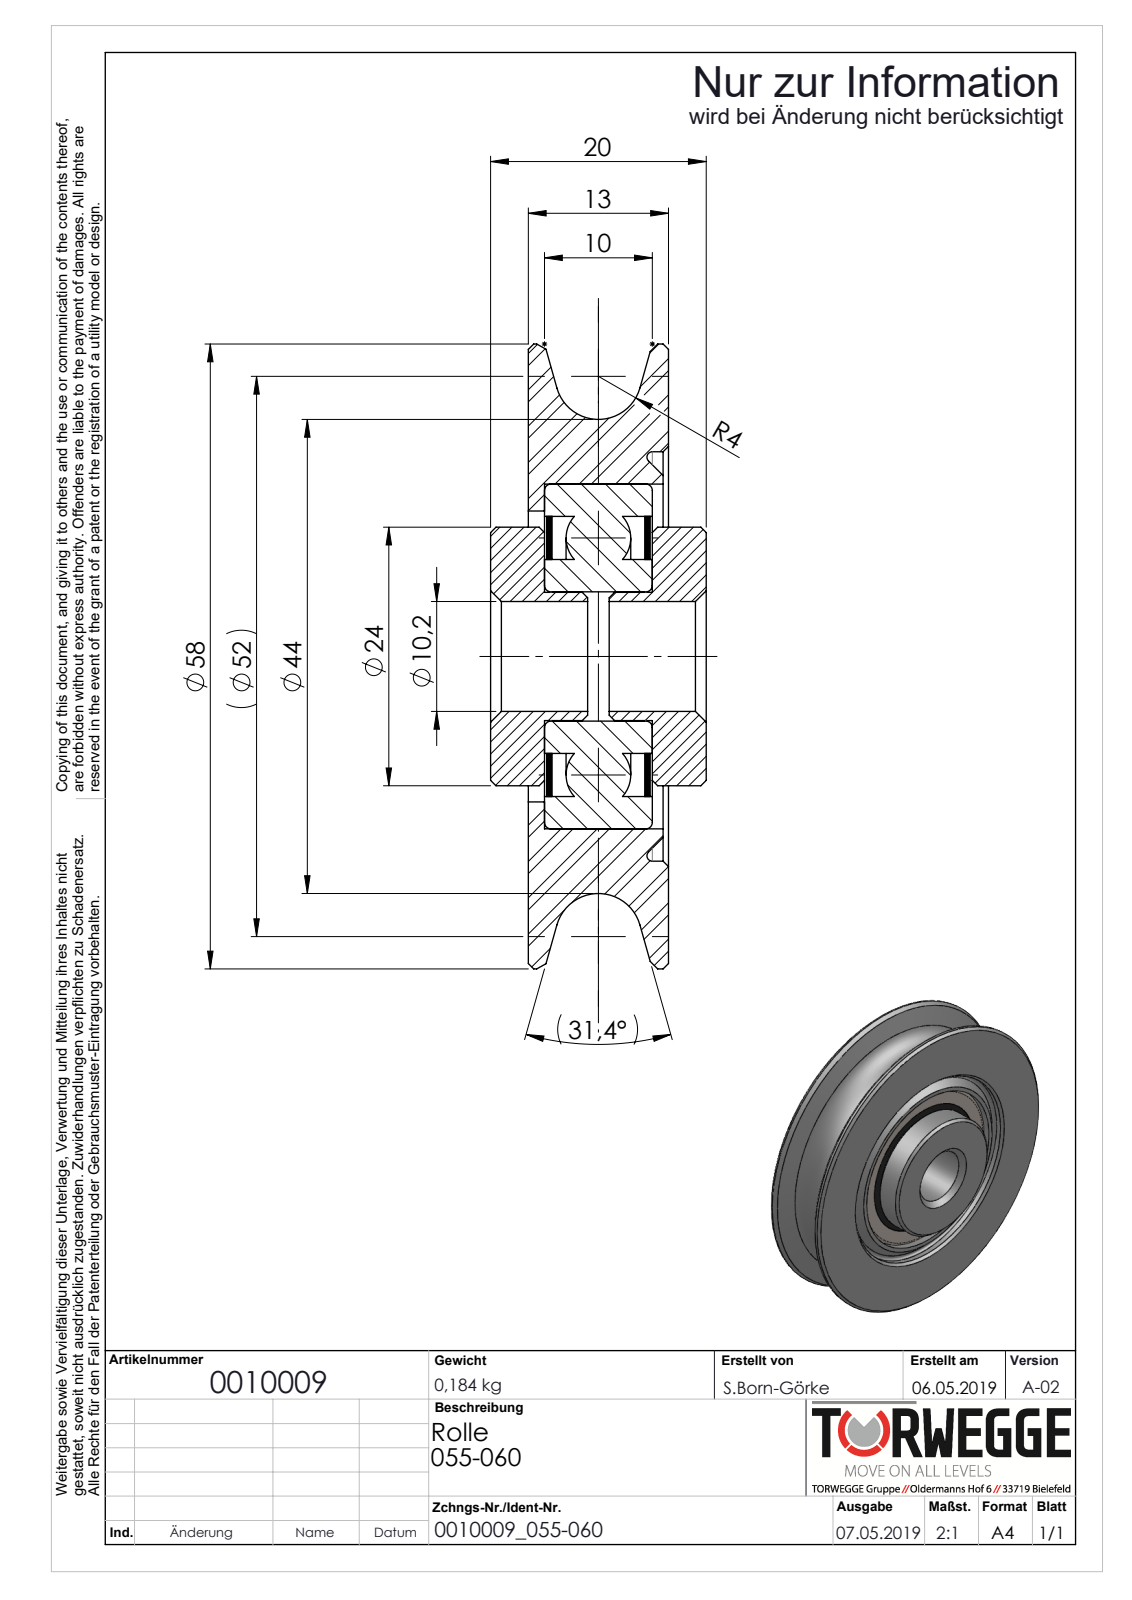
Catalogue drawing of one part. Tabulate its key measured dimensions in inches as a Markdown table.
| quantity | value |
| --- | --- |
| part name | 0010009_055-060_(A-02) |
| STEP written by | SolidWorks 2018 (AUTOMOTIVE_DESIGN) |
| units | inches |
| bodies | 0 solids, 67 faces (9 planar, 22 cylindrical, 36 other) |
| overall size | 2.283 × 2.283 × 0.787 |
| round holes (diameter × count) | 0.402 × 1, 1.024 × 1, 1.063 × 1, 1.26 × 1, 1.496 × 1 |
| round bosses / shafts (diameter × count) | 2.283 × 1, 0.945 × 1 |
| main face-to-face distances | 0.512, 0.138, 0.65, 0.205, 0.583, 0.067, 0.445, 0.197, 0.591, 0.059 |
